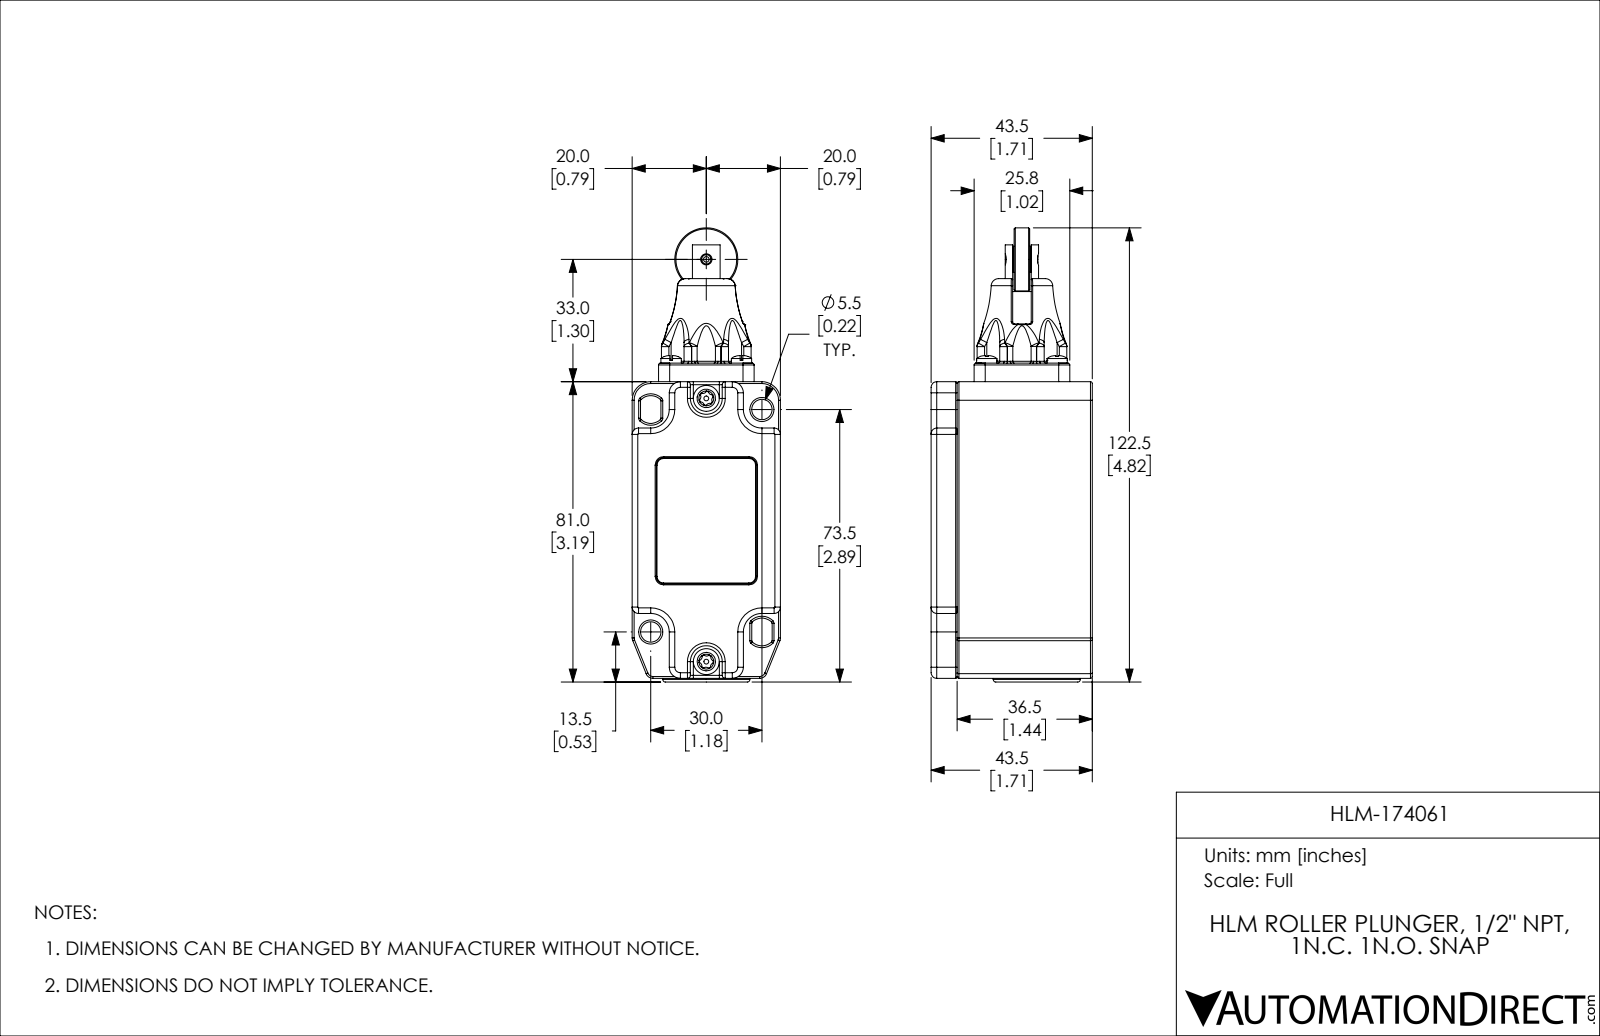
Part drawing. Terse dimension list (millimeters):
name: 174-HLM (Roller Plunger) step format
written by: SolidWorks 2013 (CONFIG_CONTROL_DESIGN)
unit: mm
bodies: 14 solids, 2264 faces (556 planar, 630 cylindrical, 1078 other)
size: 122.5 × 43.5 × 40
volume: 62 298 mm³; area: 45 647 mm²
holes: 10× ⌀3, 5× ⌀3.3, 2× ⌀3.7, 2× ⌀3.8, 2× ⌀4, 2× ⌀4.2, 2× ⌀5.5, 1× ⌀1.5, 1× ⌀2.5, 1× ⌀3.5, 1× ⌀4.4, 1× ⌀5.3
bosses: 6× ⌀6.2, 4× ⌀5.48, 3× ⌀7, 2× ⌀6.4, 2× ⌀1.3, 1× ⌀23.5, 1× ⌀18.5, 1× ⌀17.7
rounds: 173× R0.5, 26× R0.4, 25× R1, 24× R2, 18× R0.3, 14× R0.15, 12× R0.8, 10× R0.2
face distances: 2.25, 37.75, 40, 2.5, 35.5, 38.4, 40.9, 2.6, 4.4, 43.5
hole spacings: 19, 13.44, 9, 10.98, 16.51, 19.04, 21.02, 21.69
